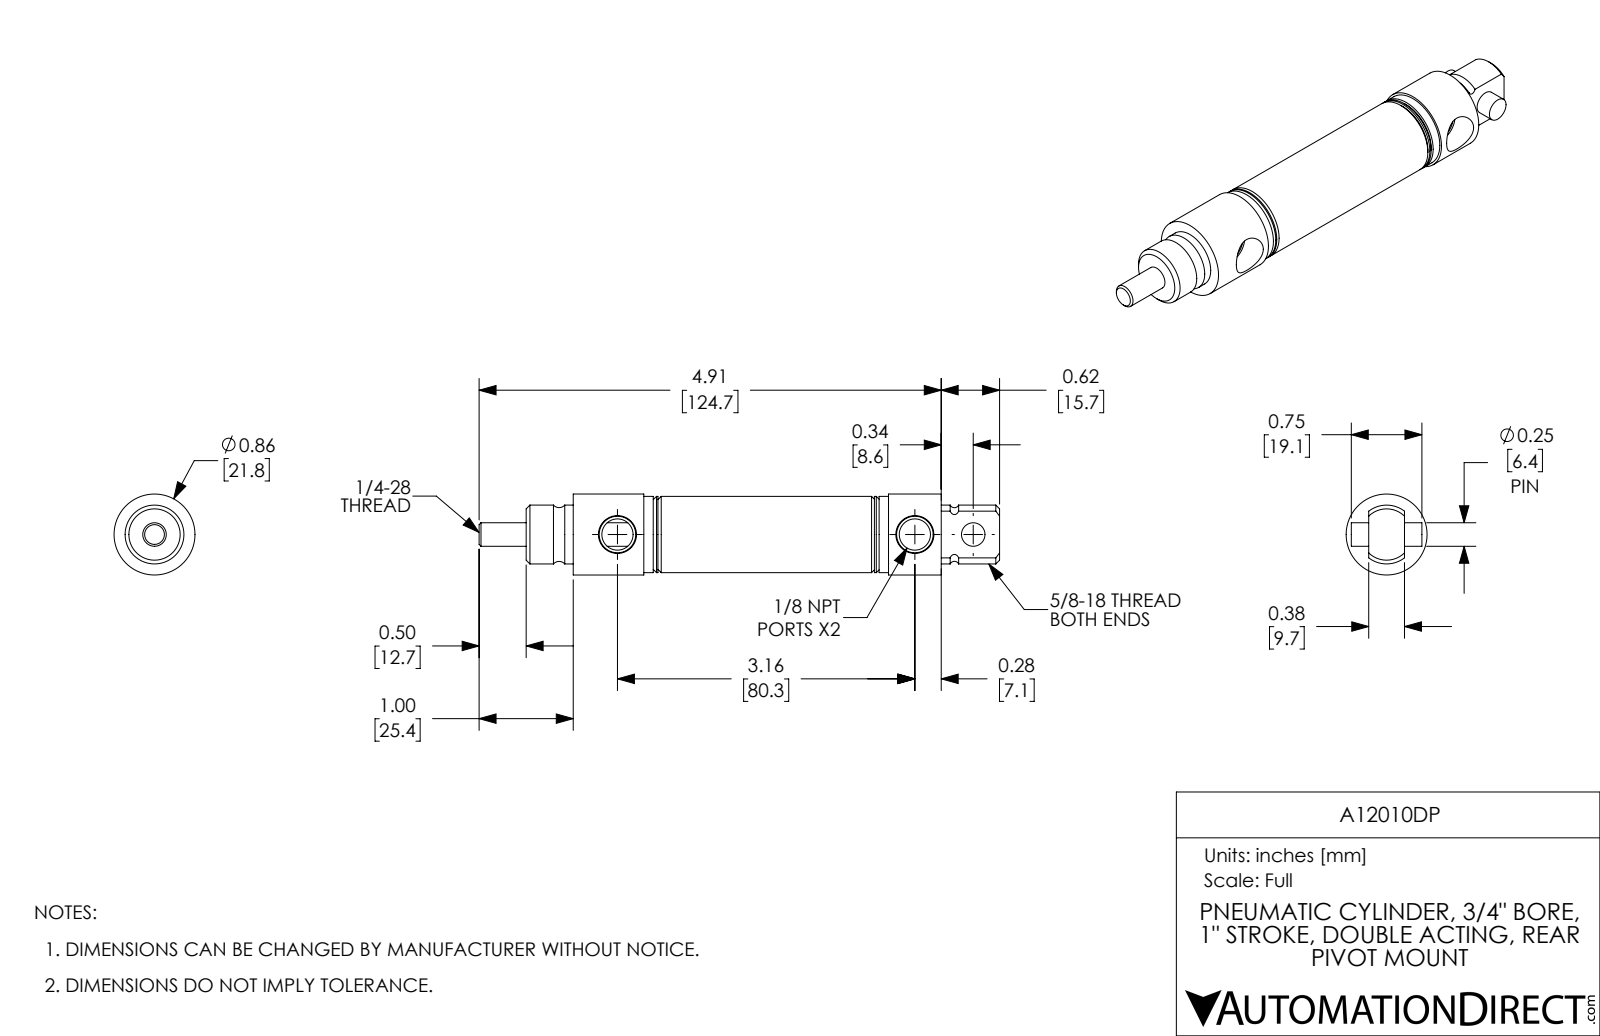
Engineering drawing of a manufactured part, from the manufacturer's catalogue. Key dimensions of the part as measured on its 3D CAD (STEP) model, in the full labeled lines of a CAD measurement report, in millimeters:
Part name (STEP PRODUCT): A12010DP; A12010DP-PIN; A12010DP-Rod; A12010DP-MainBody
STEP written by: SolidWorks 2017 (AUTOMOTIVE_DESIGN)
Units: millimetres
Bodies: 3 solids, 91 faces (21 planar, 38 cylindrical, 32 other)
Overall size (bounding box): 140.5 × 21.8 × 21.8
Volume: 31 770 mm³ · Surface area: 16 630 mm²
Round holes (diameter × count): ⌀6.4 ×2, ⌀8.4 ×2, ⌀19.1 ×1
Round bosses / shafts (diameter × count): ⌀21.8 ×1, ⌀20.6 ×1, ⌀15.9 ×1
Main face-to-face distances: 12.7, 68.7, 25.4, 38.1, 30.6, 43.3, 68.7, 56, 99.3, 30.6
Hole centre spacings: 15.7, 80.3, 96
